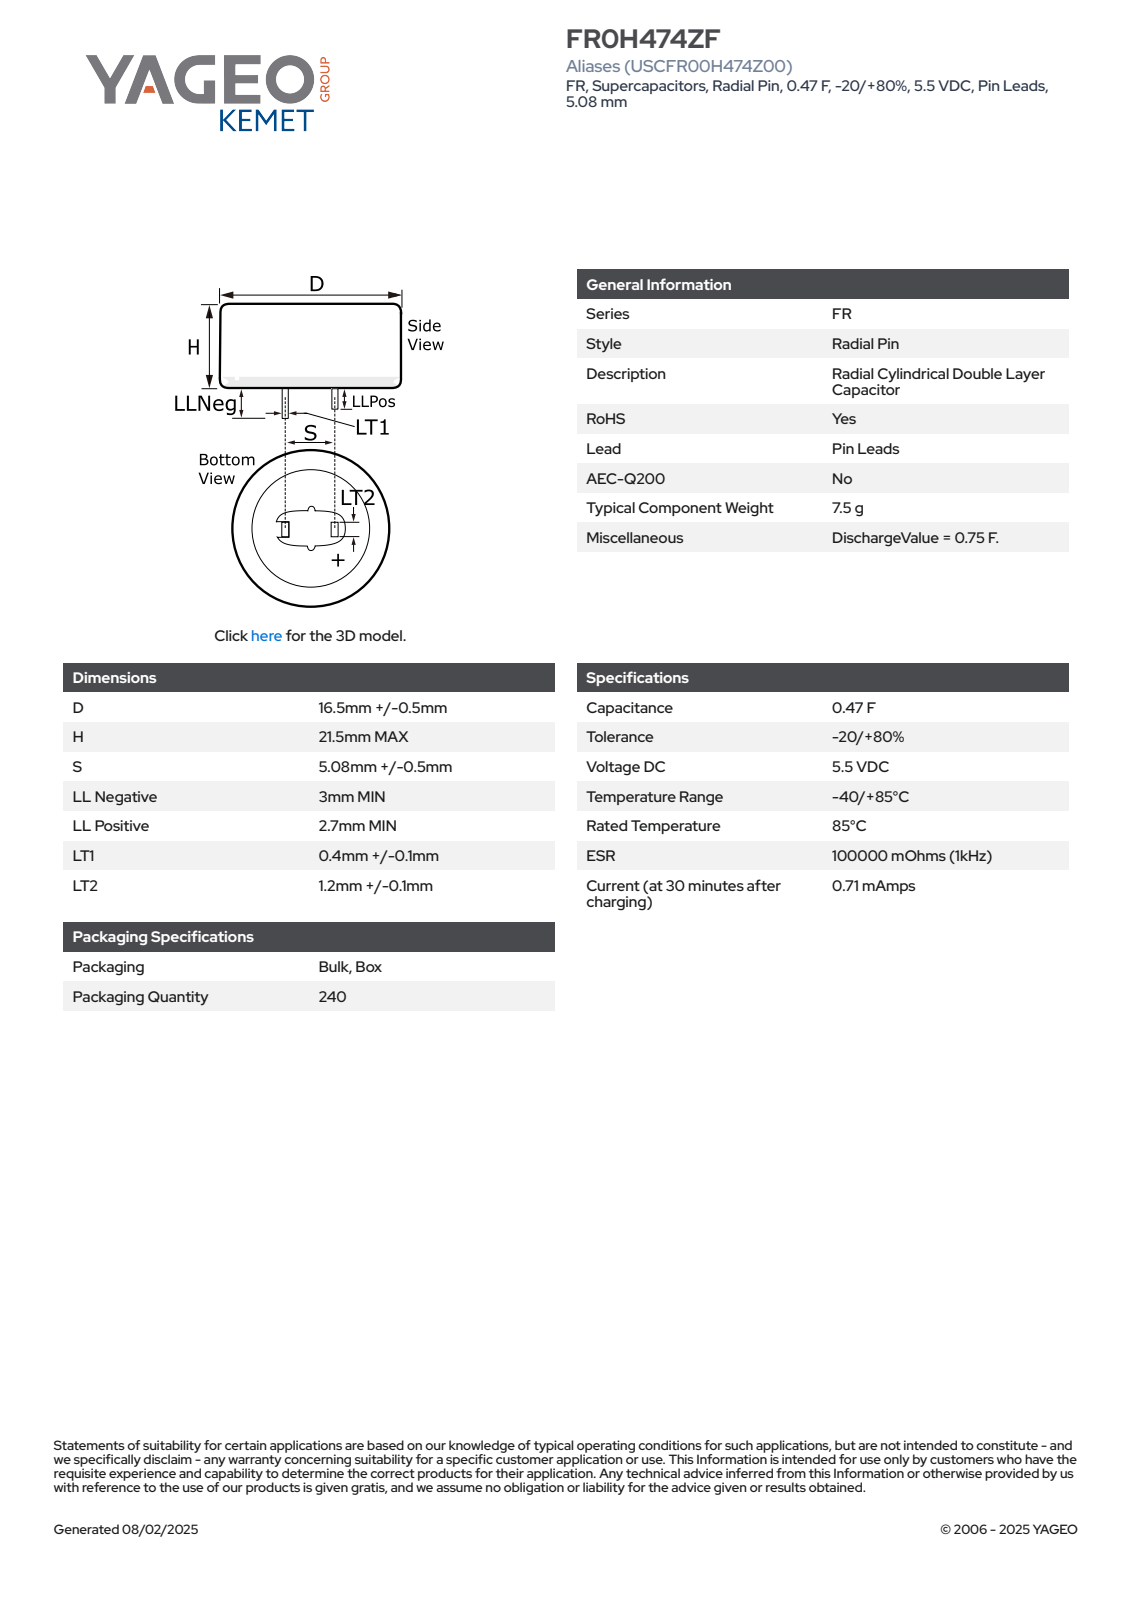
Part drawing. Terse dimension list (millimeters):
name: CDR_LPLLN_D17L21.5S5.08LLNEG3LLPOS2.7LT10.5LT21.3
written by: SolidWorks 2014 (AUTOMOTIVE_DESIGN)
unit: mm
bodies: 1 solid, 78 faces (70 planar, 4 cylindrical, 4 other)
size: 24.5 × 17 × 17
volume: 4 842 mm³; area: 1 558 mm²
bosses: 1× ⌀17
rounds: 1× R8.51
face distances: 21.5, 21.49, 0.5, 5.08, 5.58, 4.58, 1.3, 3, 24.49, 24.5
